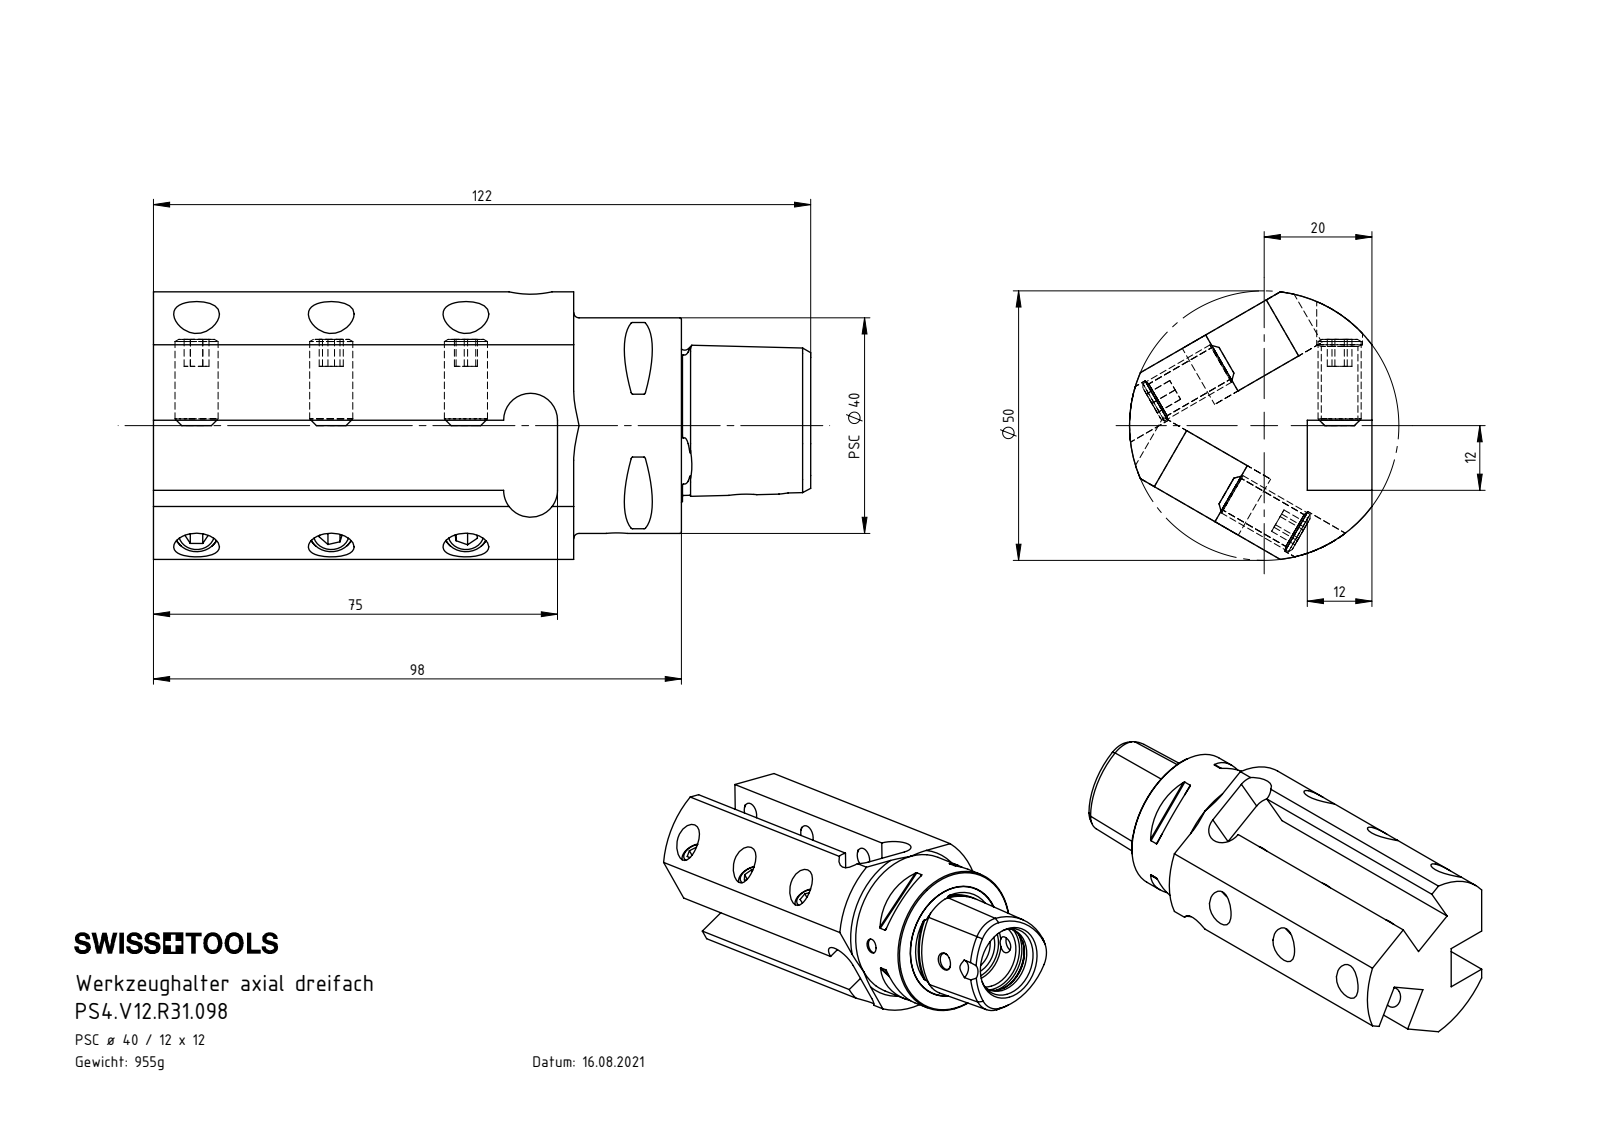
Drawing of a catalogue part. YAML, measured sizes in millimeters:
part_name: "ISO 4026 - M8 x 16_PreviewCfg; PS4-V12.R31.098_A; PS4-V12.R31.098"
step_written_by: "SolidWorks 2017 (CONFIG_CONTROL_DESIGN)"
units: millimeters
bodies: {solids: 10, faces: 261, planar: 122, cylindrical: 55, other: 84}
overall_size: [122, 49.64, 45]
volume: 121664
surface_area: 35471
round_holes:
  - {diameter: 8.5, count: 10}
  - {diameter: 6.8, count: 9}
  - {diameter: 4, count: 1}
  - {diameter: 4.6, count: 1}
  - {diameter: 5, count: 1}
  - {diameter: 12.5, count: 1}
  - {diameter: 18, count: 1}
  - {diameter: 20, count: 1}
round_bosses_or_shafts:
  - {diameter: 8, count: 9}
  - {diameter: 40, count: 1}
partial_cylinders:
  - {radius: 0.3, count: 8}
  - {radius: 5, count: 6}
  - {radius: 3, count: 1}
  - {radius: 25, count: 1}
face_to_face_distances: [12, 13, 23, 75, 98, 20, 3, 78, 4, 15]
hole_center_spacings: [25, 50, 23.5, 31.3, 53.37, 54.82, 77.77, 79.25]
